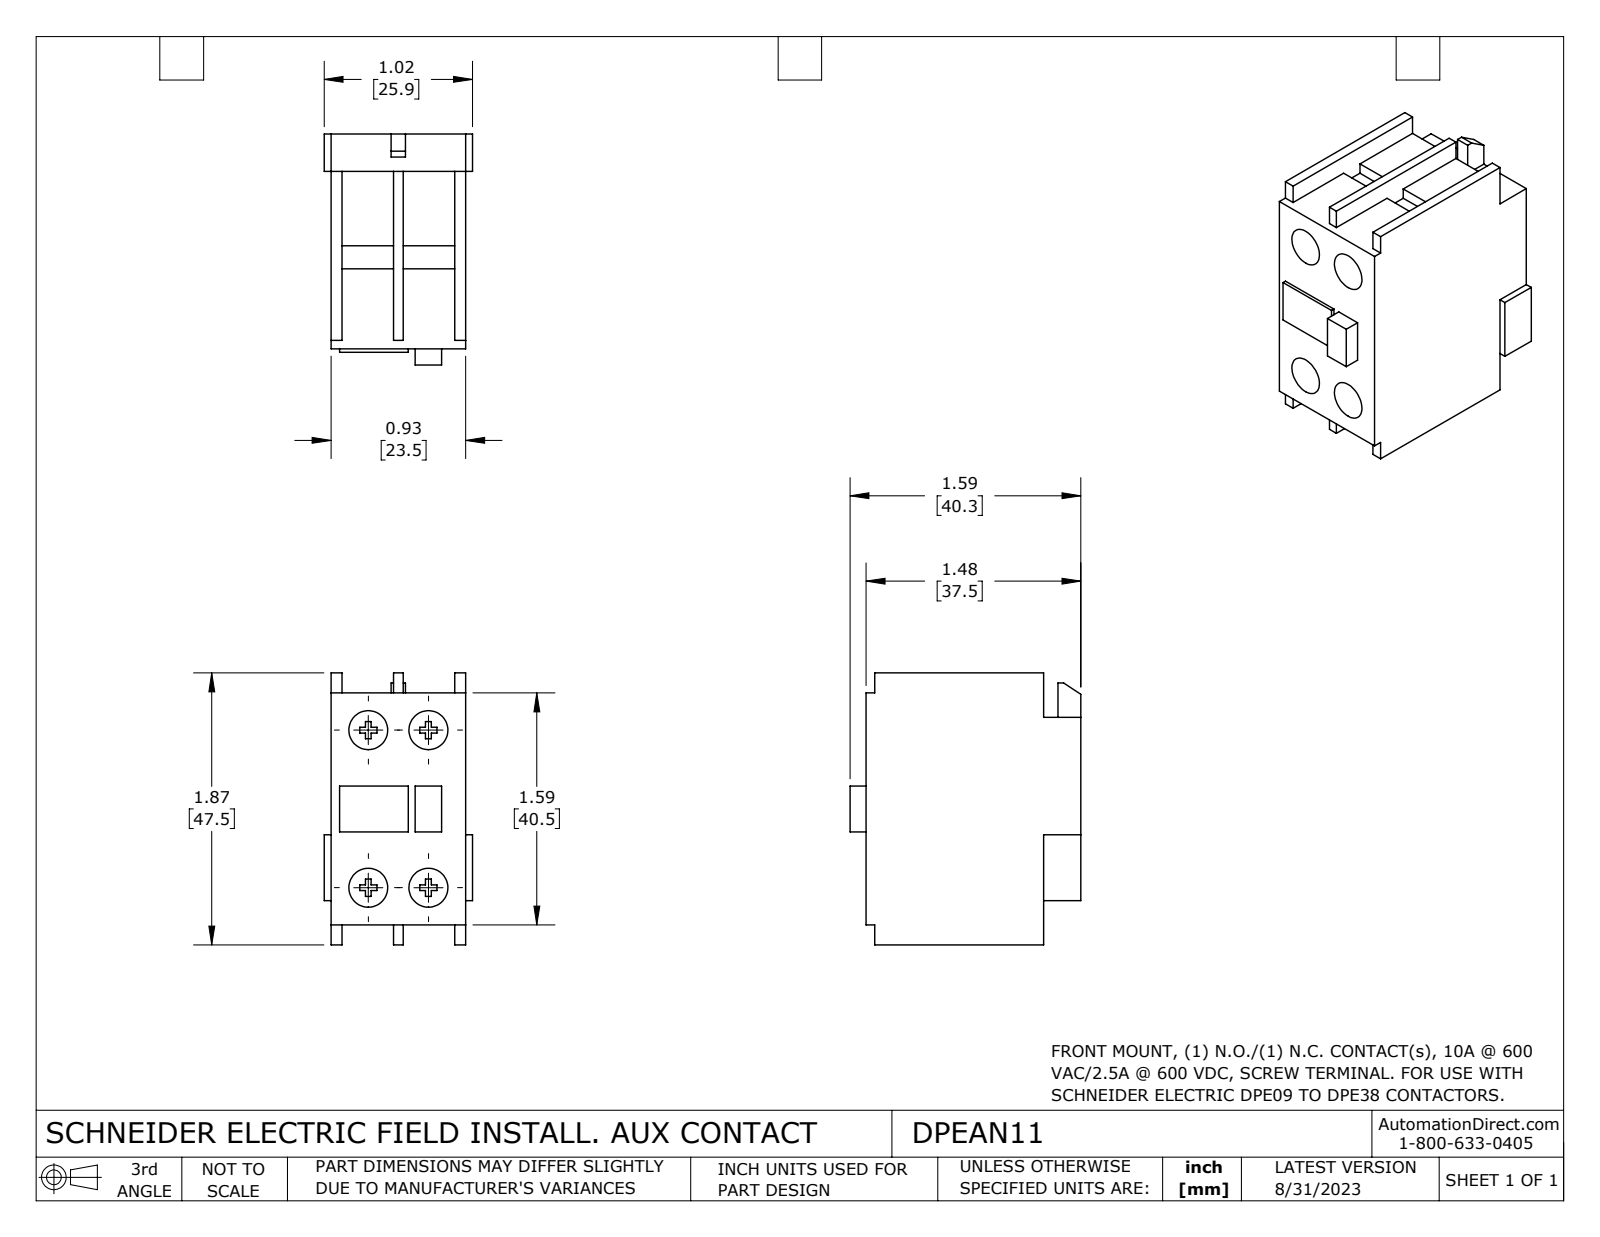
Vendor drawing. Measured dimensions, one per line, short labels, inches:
name: DPEAN11
written by: SolidWorks 2021 (CONFIG_CONTROL_DESIGN)
unit: in
bodies: 1 solid, 131 faces (123 planar, 8 cylindrical, 0 other)
size: 1.87 × 1.587 × 1.02
volume: 2.08 in³; area: 14.43 in²
holes: 4× ⌀0.268
face distances: 0.925, 1.476, 1.594, 0.354, 0.075, 0.429, 0.496, 0.85, 0.421, 0.138
hole spacings: 0.413, 1.083, 1.159
